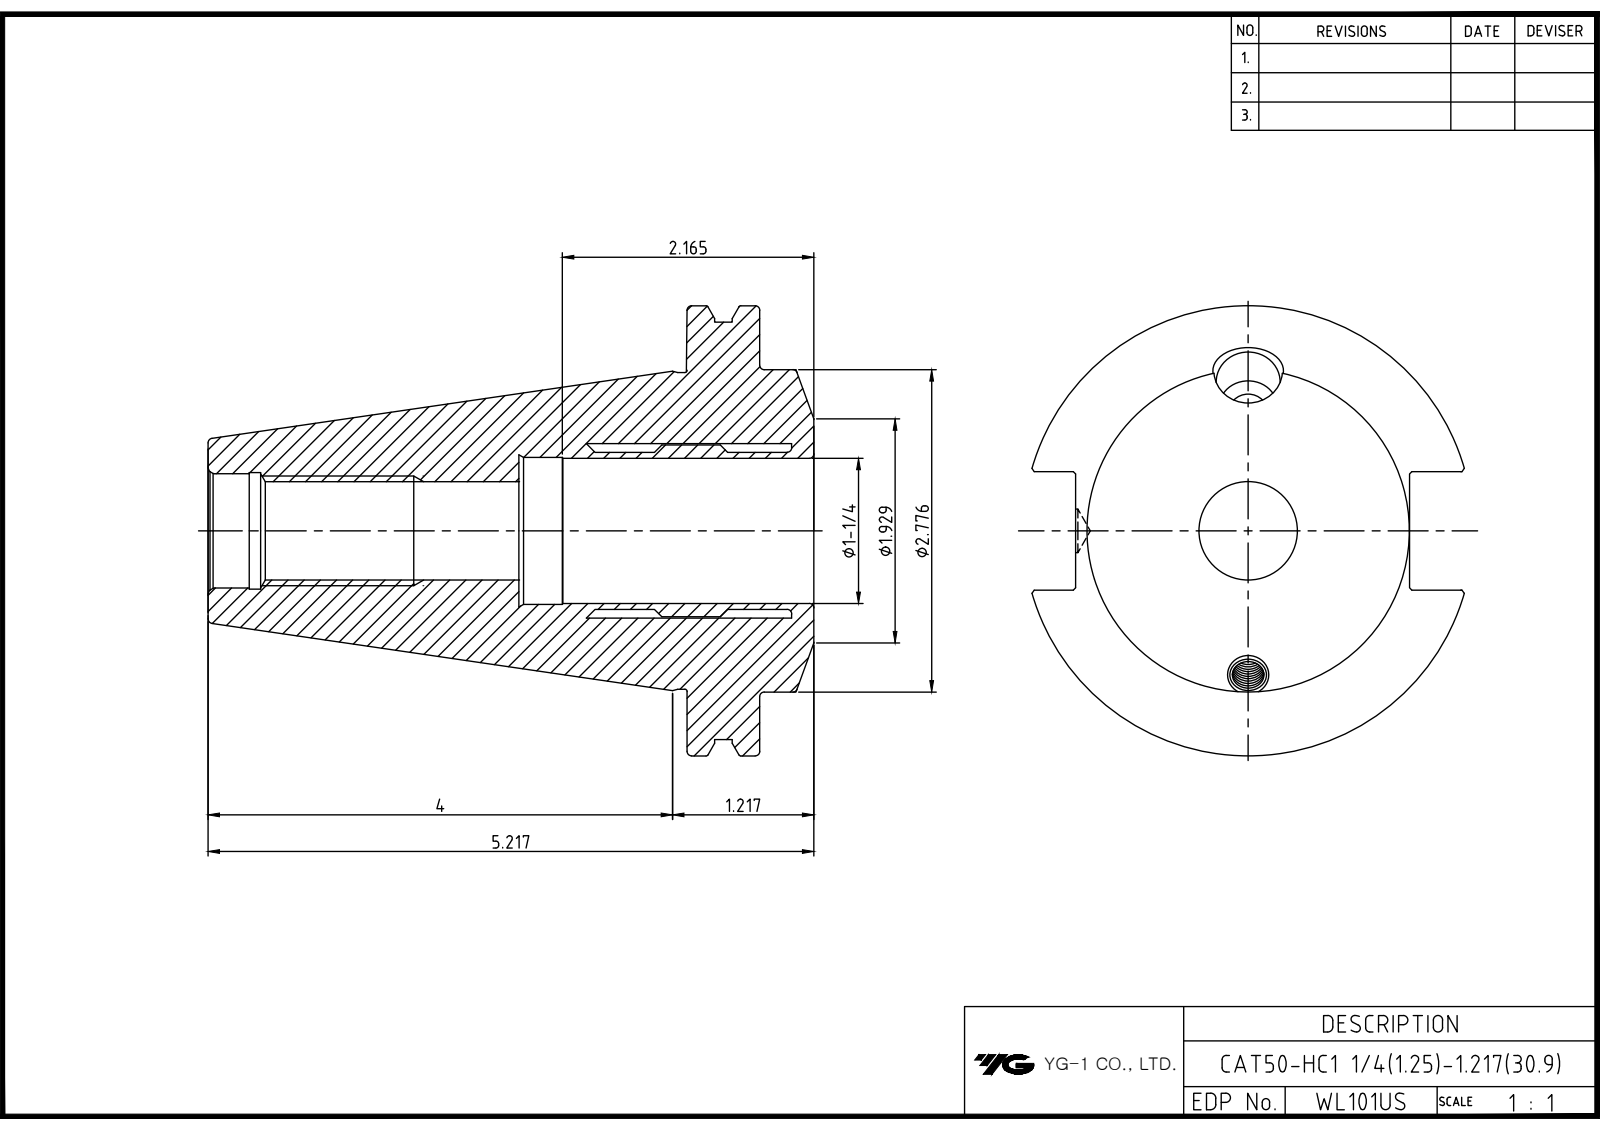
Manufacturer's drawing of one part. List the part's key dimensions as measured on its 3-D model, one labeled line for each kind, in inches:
Part name (STEP PRODUCT): LO-CAT50-HC31.75-30.9
STEP written by: Autodesk Inventor 2022 (AUTOMOTIVE_DESIGN)
Units: inches
Bodies: 1 solid, 57 faces (28 planar, 12 cylindrical, 17 other)
Overall size (bounding box): 5.217 × 3.875 × 3.728
Volume: 20.21 in³ · Surface area: 74.72 in²
Round holes (diameter × count): ⌀0.375 ×1, ⌀0.865 ×1, ⌀1.031 ×1, ⌀1.25 ×1
Round bosses / shafts (diameter × count): ⌀3.875 ×1, ⌀3.594 ×1, ⌀2.776 ×1, ⌀2.726 ×1
Main face-to-face distances: 0.625, 1.092, 0.467, 4.125, 4.75, 5.217, 2.815, 1.31, 1.935, 2.402
